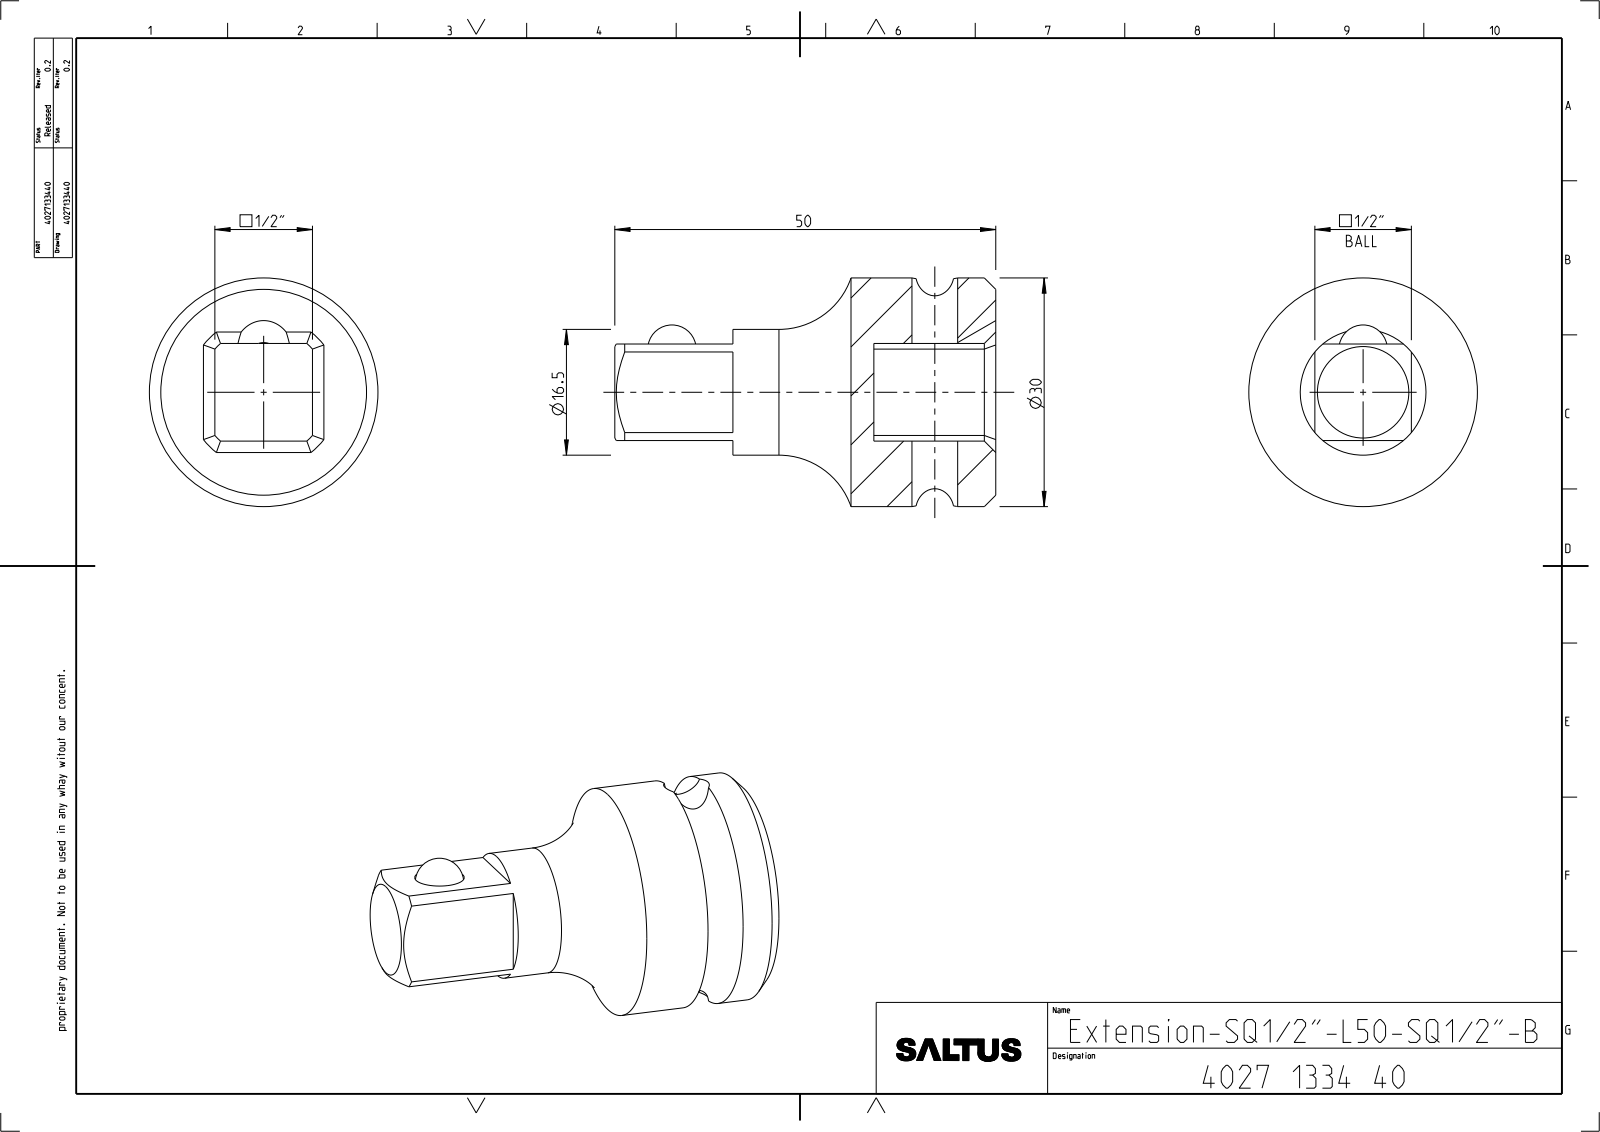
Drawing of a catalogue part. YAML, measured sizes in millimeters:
part_name: "4027133440"
step_written_by: "CREO PARAMETRIC BY PTC INC, 2022414 (CONFIG_CONTROL_DESIGN)"
units: millimeters
bodies: {solids: 2, faces: 58, planar: 21, cylindrical: 17, other: 20}
overall_size: [50, 30, 30]
volume: 16079
surface_area: 5929
round_holes:
  - {diameter: 6, count: 1}
  - {diameter: 6.5, count: 1}
round_bosses_or_shafts:
  - {diameter: 30, count: 1}
  - {diameter: 16.5, count: 1}
partial_cylinders:
  - {radius: 4, count: 1}
  - {radius: 8.55, count: 1}
face_to_face_distances: [12.74, 12.82, 12.66, 16, 50, 34, 34.5, 18.5, 15.5, 6.41]
hole_center_spacings: [34.5]
